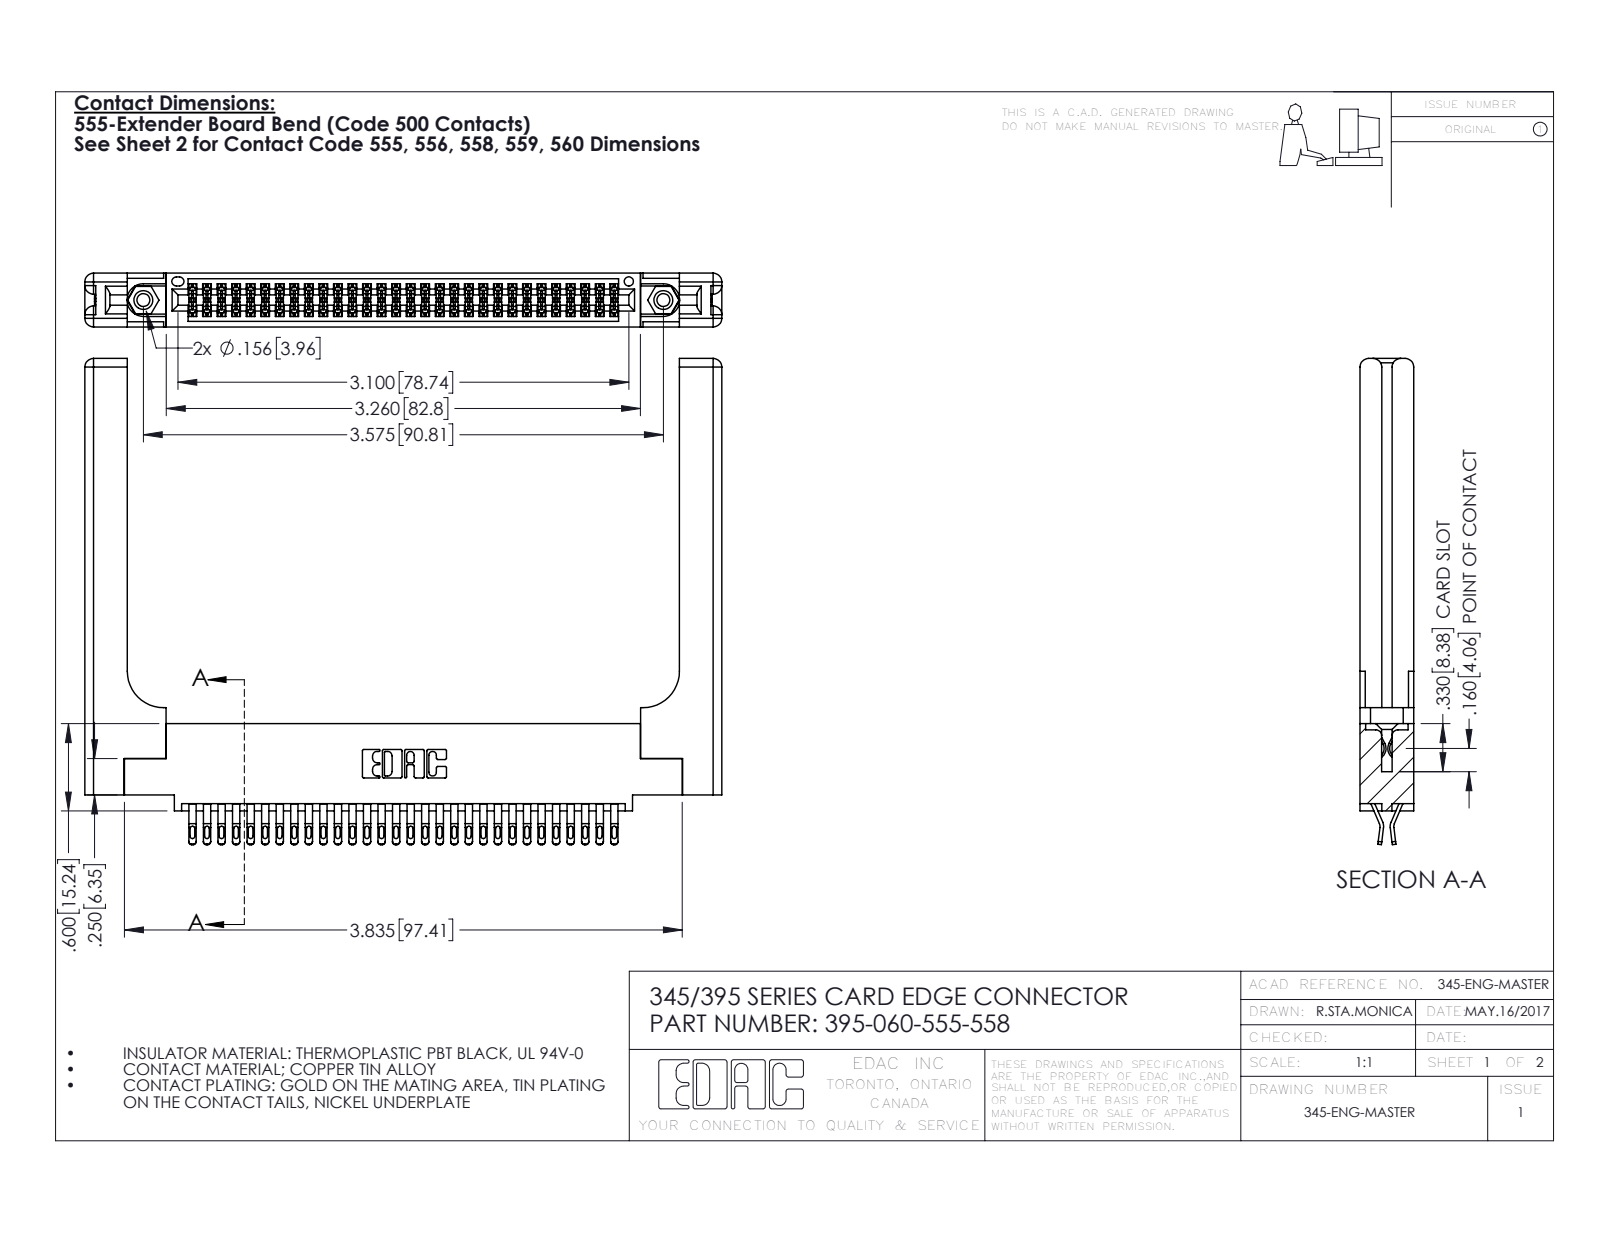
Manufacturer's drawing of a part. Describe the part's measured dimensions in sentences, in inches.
The part is named "395-060-555-558; 345-250-001_345-250-001-102; 345-292-001_555 Tail; 345-220-058_345-220-058 (+1 more)". Its 3-D file was written by "SolidWorks 2016 (CONFIG_CONTROL_DESIGN)". It is 65 solids with 3746 faces: 2092 planar, 1594 cylindrical and 60 other. Overall it measures 4.379 by 3.342 by 0.37 inches. Its volume is 1.176 cubic inches and its surface area 33.29 square inches. Round holes: 2 of diameter 0.089, 2 of diameter 0.125, 2 of diameter 0.156, 1 of diameter 0.064. Round bosses or shafts: 2 of diameter 0.155. Partial cylindrical surfaces (rounded edges, fillets, slot ends): 150 of radius 0.016, 120 of radius 0.02, 90 of radius 0.006, 22 of radius 0.01, 16 of radius 0.06, 6 of radius 0.007, 6 of radius 0.031, 3 of radius 0.026. The main face-to-face distances are 0.37, 0.072, 0.298, 0.025, 0.225, 0.098, 0.272, 0.2, 0.148, 0.15. The hole center spacings are 0.27, 3.34, 3.575.
